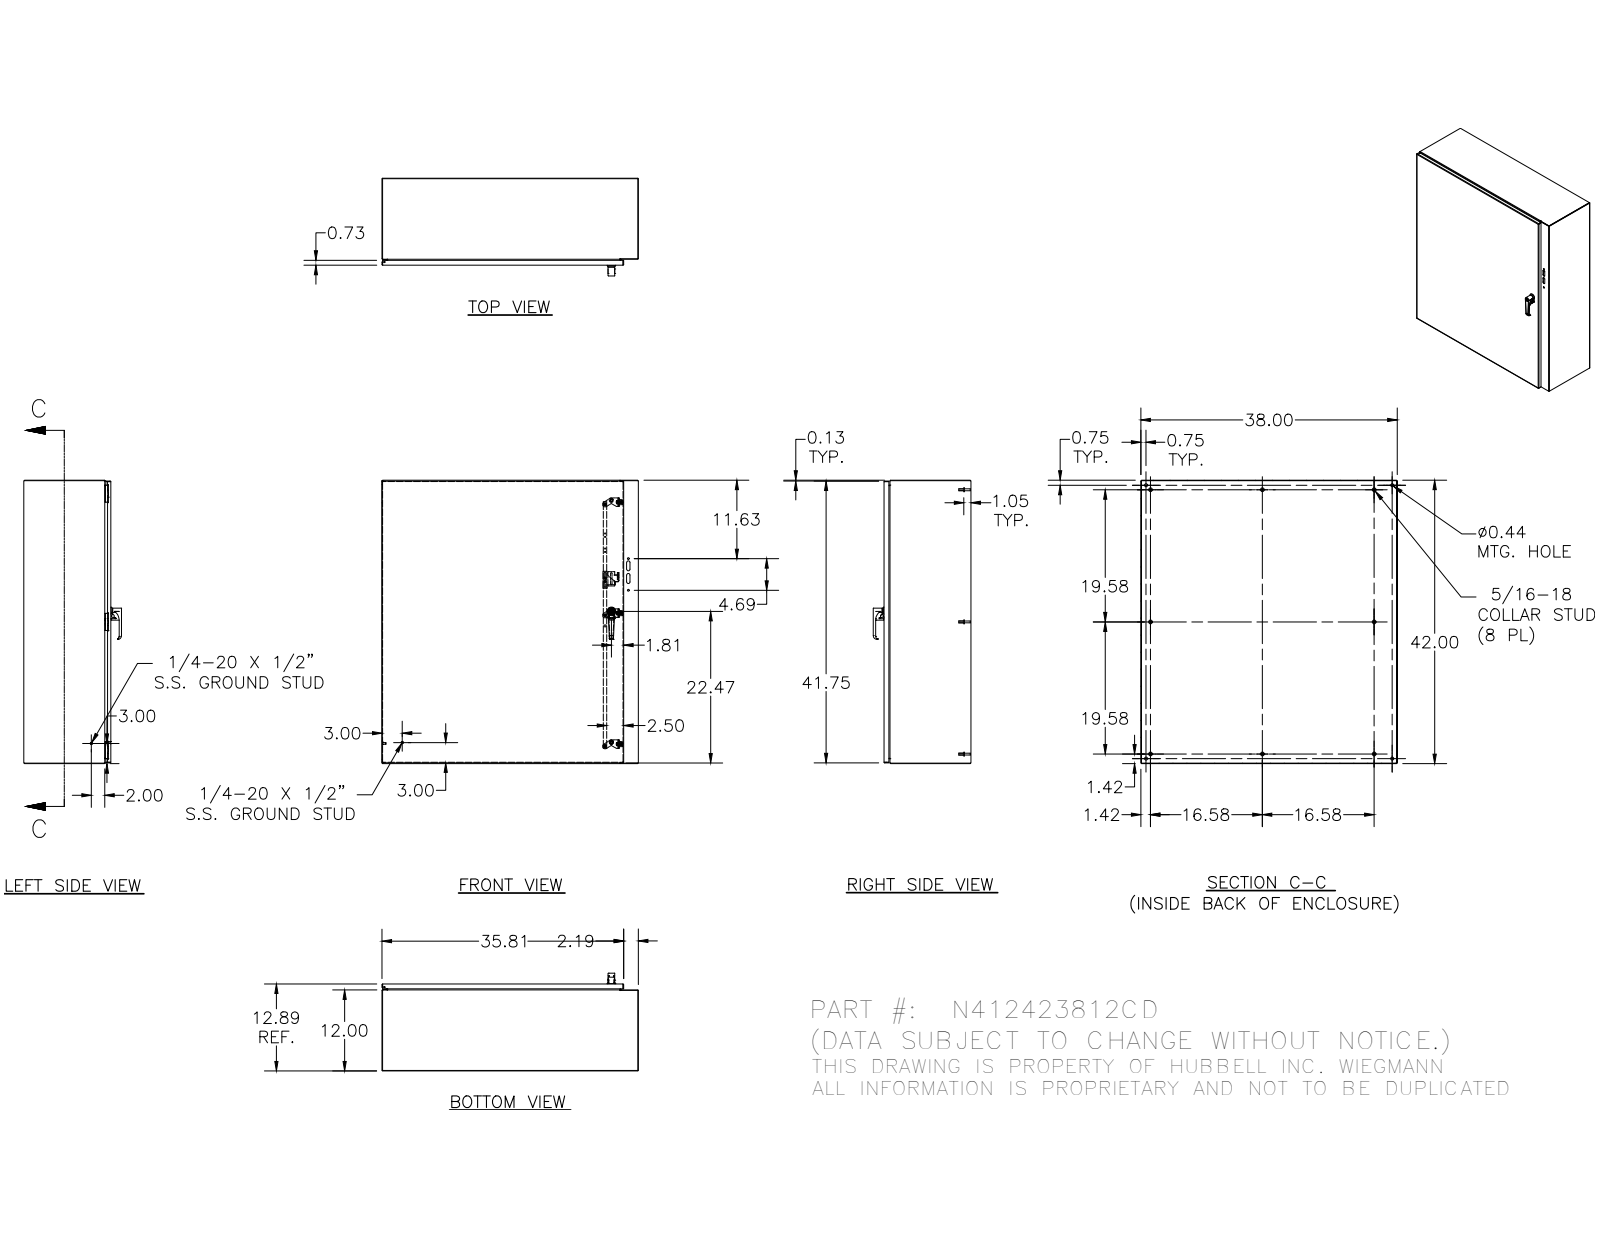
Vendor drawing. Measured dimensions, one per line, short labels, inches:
name: N412423812CD
written by: SolidWorks 2019 (AUTOMOTIVE_DESIGN)
unit: in
bodies: 83 solids, 2647 faces (1023 planar, 964 cylindrical, 660 other)
size: 42 × 38 × 14.512
volume: 409.4 in³; area: 11 002 in²
holes: 7× ⌀0.188, 6× ⌀0.093, 6× ⌀0.145, 6× ⌀0.152, 6× ⌀0.167, 6× ⌀0.172, 5× ⌀0.156, 4× ⌀0.32, 4× ⌀0.438, 3× ⌀0.196, 3× ⌀0.211, 3× ⌀0.22
bosses: 16× ⌀0.25, 14× ⌀0.3, 8× ⌀0.563, 6× ⌀0.437, 6× ⌀0.36, 6× ⌀0.32, 6× ⌀0.256, 6× ⌀0.164
rounds: 38× R0.02, 38× R0.05, 37× R0.125, 30× R0.012, 26× R0.016, 24× R0.025, 18× R0.031, 14× R0.016
face distances: 0.074, 12.843, 12.769, 12.917, 37.926, 41.926, 37.852, 38, 41.852, 42
hole spacings: 19, 16.789, 19.211, 0.5, 36, 38, 19.007, 0.656
